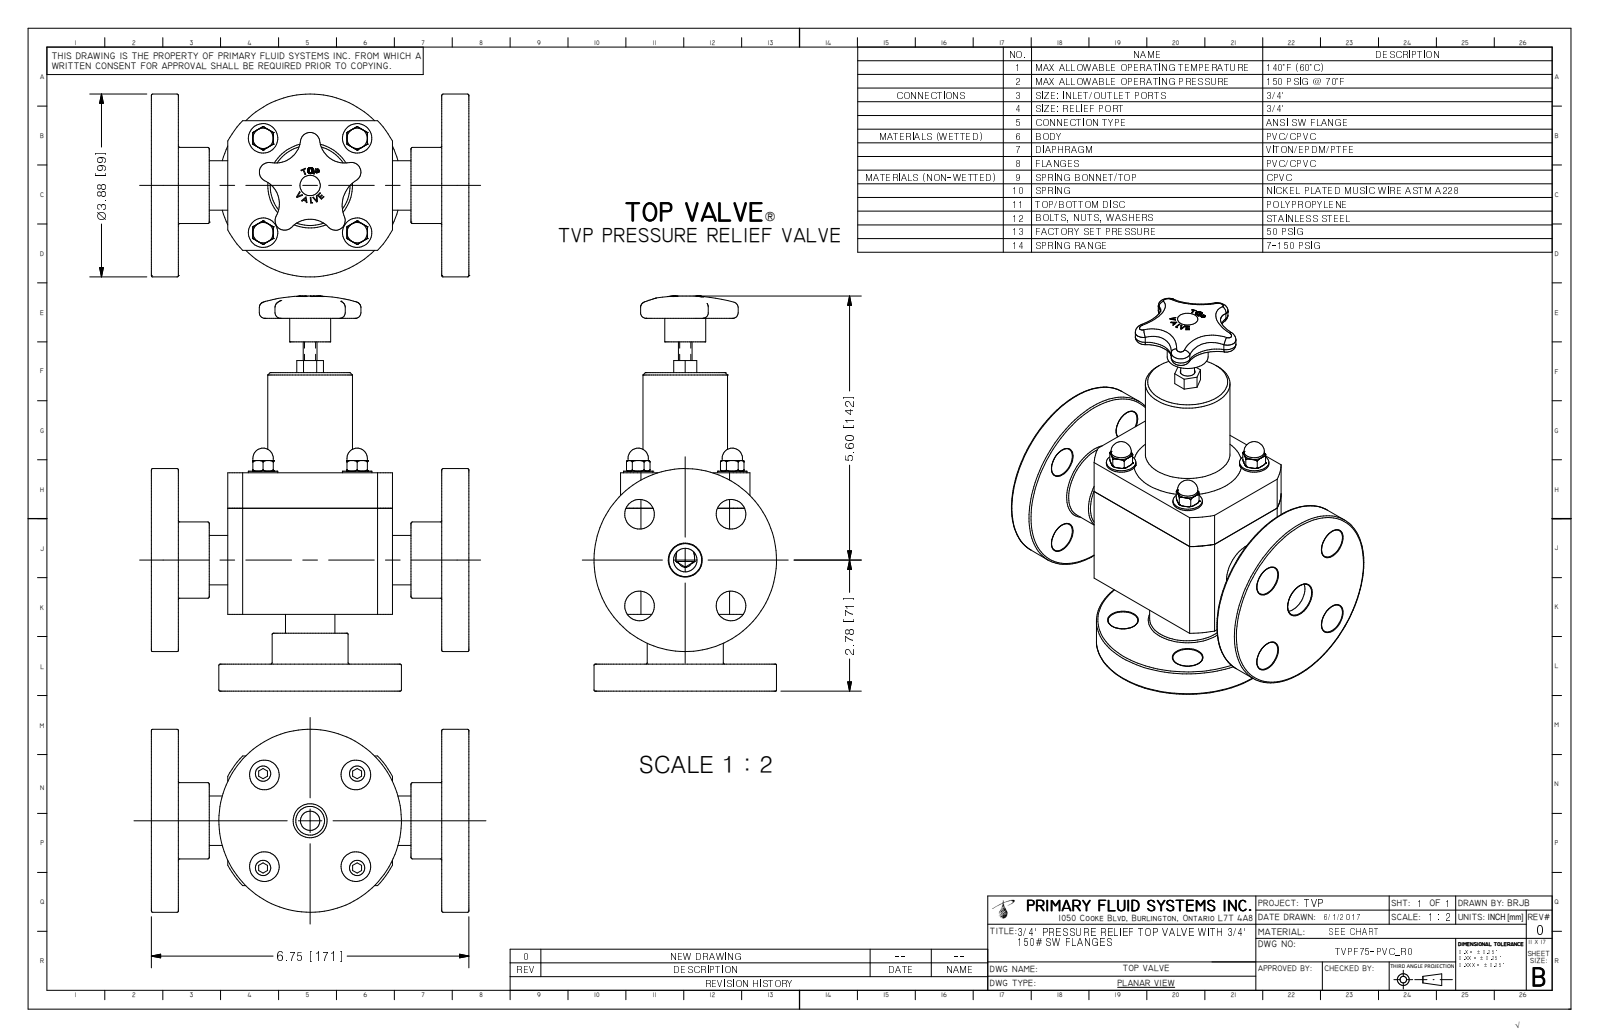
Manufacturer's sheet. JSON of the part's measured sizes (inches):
{"part_name": "TVPF75-PVC_R0", "step_written_by": "Autodesk Inventor 2009 (AUTOMOTIVE_DESIGN)", "units": "inches", "bodies": {"solids": 1, "faces": 416, "planar": 160, "cylindrical": 68, "other": 188}, "overall_size": [8.38, 6.75, 3.88], "volume_in3": 55.74, "surface_area_in2": 219.5, "round_holes": [[0.63, 8], [0.175, 4], [0.722, 2], [0.742, 2], [2.4, 1]], "round_bosses_or_shafts": [[0.625, 4], [0.433, 4], [3.88, 2], [1.616, 2], [1.05, 2], [2.375, 1], [1.8, 1], [0.87, 1]], "partial_cylinders_radius": [[0.085, 5], [0.205, 5], [0.536, 4], [0.656, 4], [0.625, 1], [0.745, 1], [1.988, 1]], "face_to_face_distances": [0.575, 6.175, 5.125, 6.75, 1.05, 1.625, 4.55, 2.75, 1.63, 0.575], "hole_center_spacings": [1.375, 1.945, 1.972, 0.039, 1.414, 2, 2.75, 2.789]}
